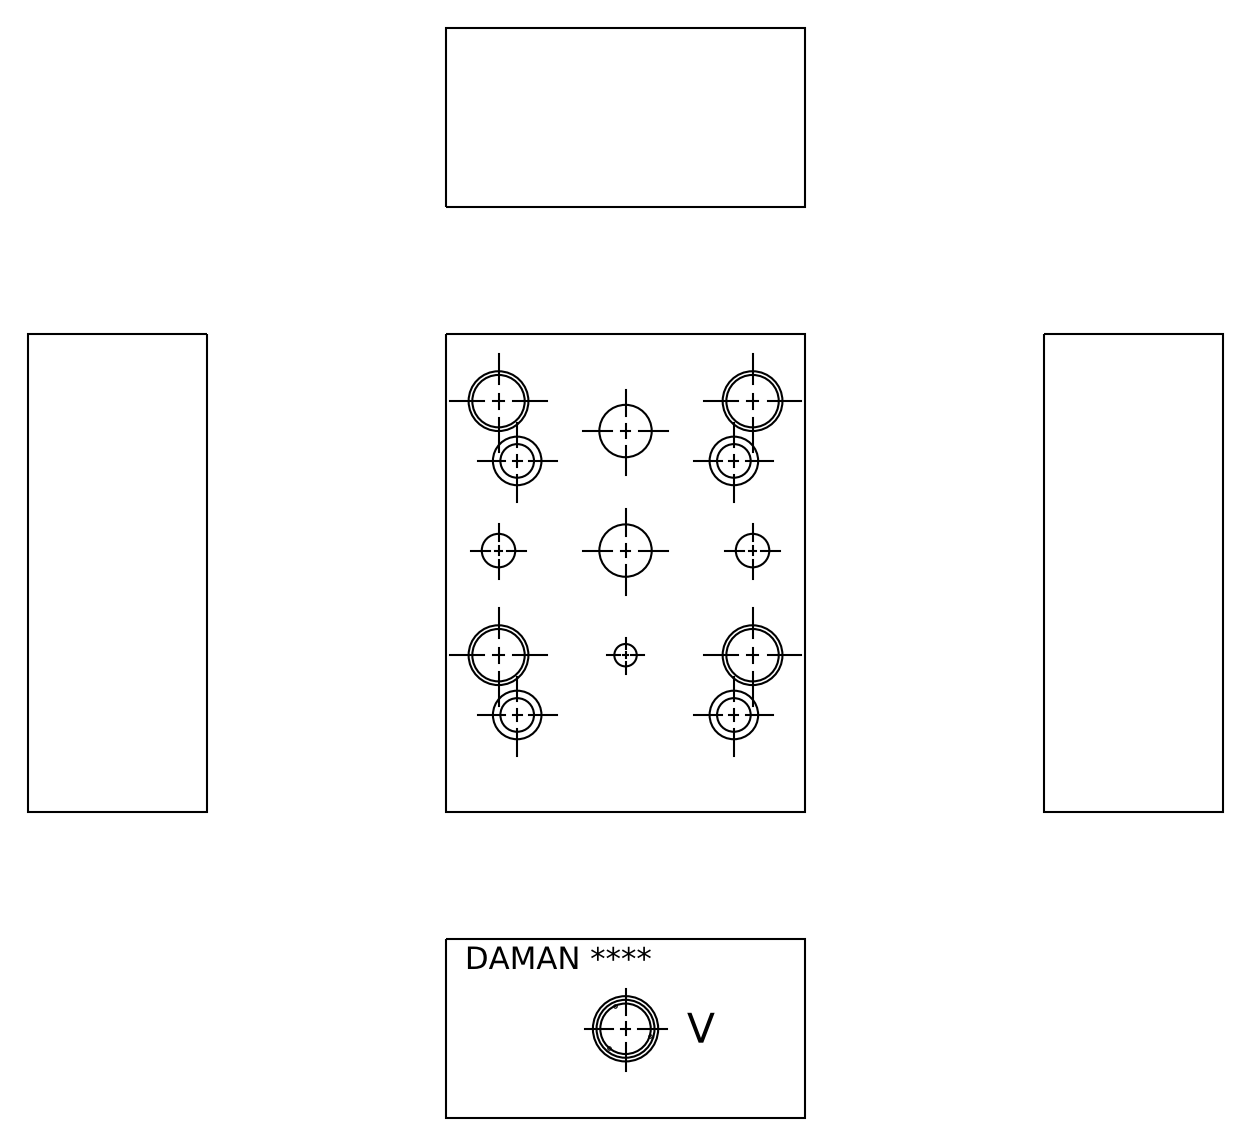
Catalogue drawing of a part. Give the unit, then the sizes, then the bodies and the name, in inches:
Units: inches
Overall size (bounding box): 4 × 3 × 1.5
Round holes (diameter × count): ⌀0.625 ×6, ⌀0.422 ×5, ⌀0.438 ×5, ⌀0.406 ×4, ⌀0.5 ×4, ⌀0.281 ×2, ⌀0.188 ×1, ⌀0.546 ×1
Partial cylindrical surfaces — rounded edges, fillets, slot ends (radius × count): R0.141 ×8, R0.187 ×1, R0.313 ×1
Main face-to-face distances: 1.5, 3, 4, 0.052, 1.448, 1.125, 1.073, 0.375, 0.44, 0.388
Hole centre spacings: 0.875, 2.121, 0.523, 1.059, 1.062, 1.246, 1.374, 1.376
Volume: 16.23 in³ · Surface area: 60.7 in²
Bodies: 1 solid, 400 faces (271 planar, 38 cylindrical, 91 other)
Part name (STEP PRODUCT): Part_DI06D05HRVA_3D
STEP written by: Autodesk Inventor 2020 (AUTOMOTIVE_DESIGN)
